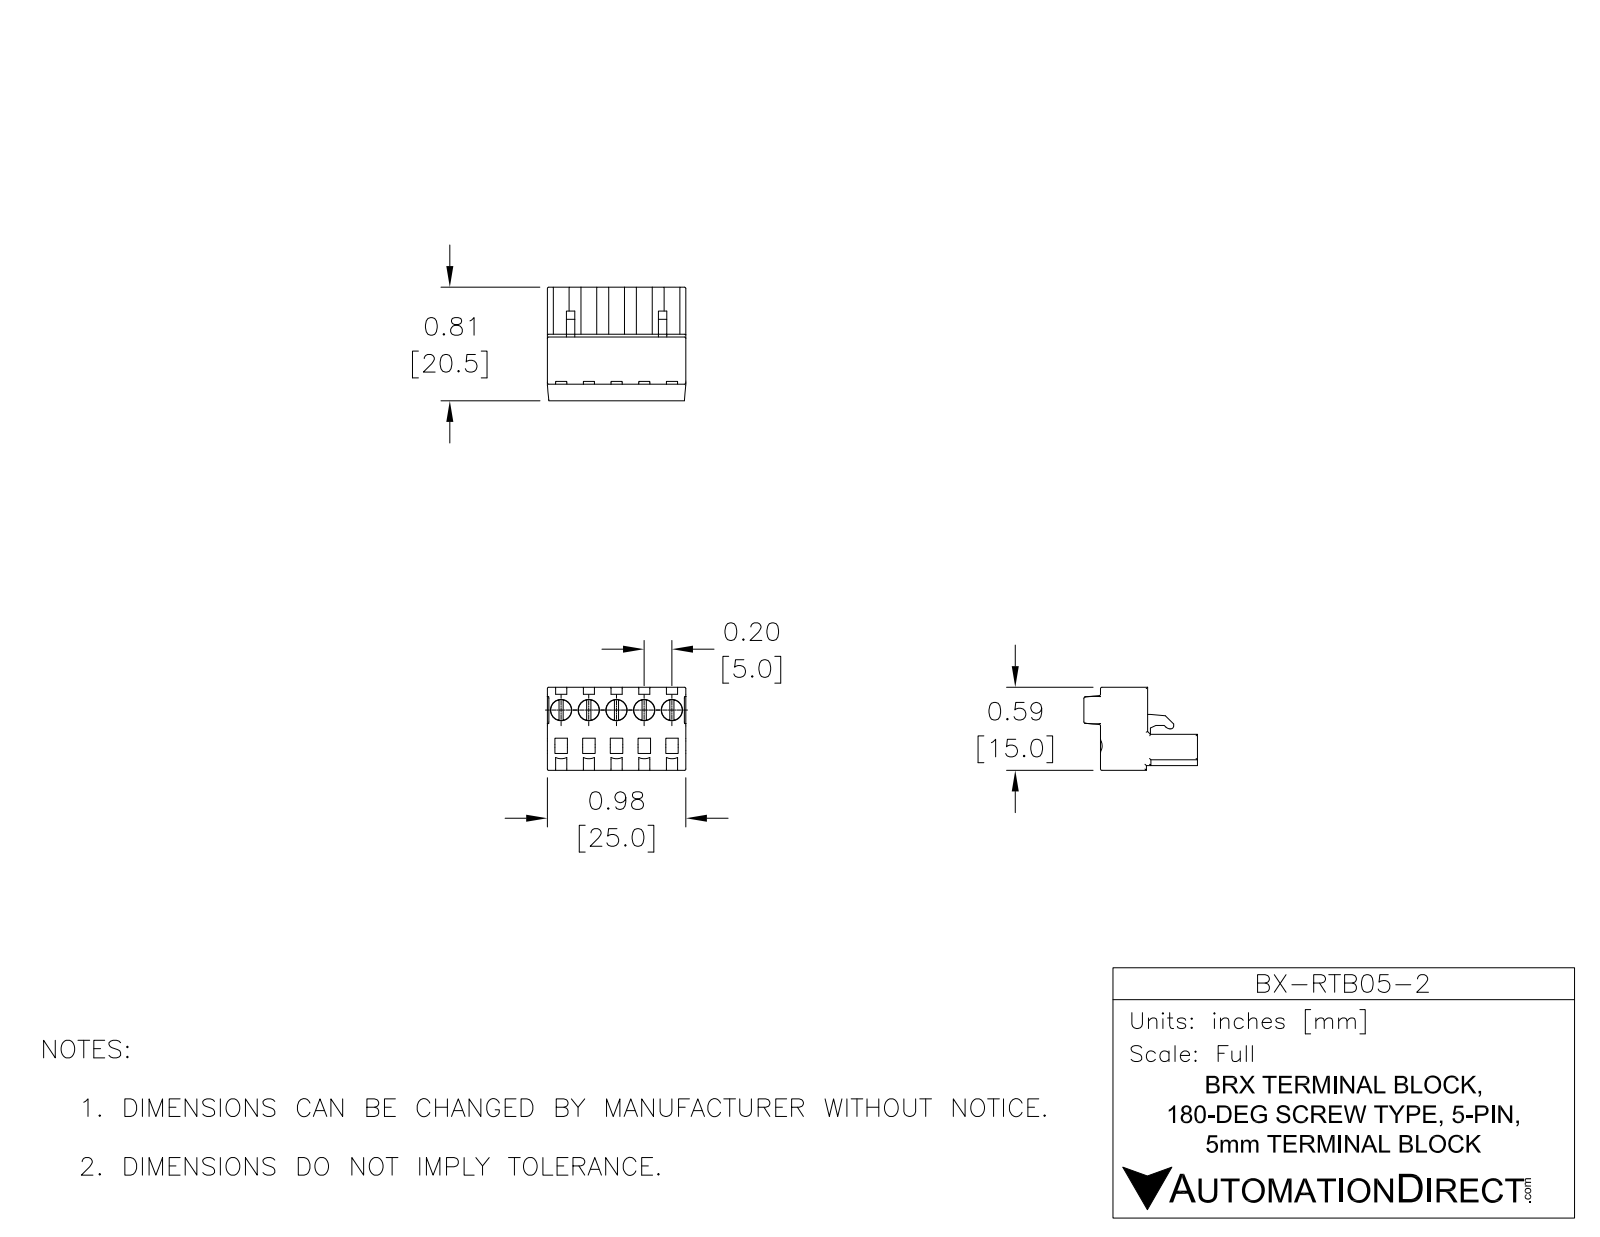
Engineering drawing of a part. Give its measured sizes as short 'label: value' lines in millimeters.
name: BX-RTB05-2
written by: SolidWorks 2016 (AUTOMOTIVE_DESIGN)
unit: mm
bodies: 1 solid, 372 faces (207 planar, 102 cylindrical, 63 other)
size: 25 × 20.5 × 15
volume: 4 195 mm³; area: 3 111 mm²
holes: 5× ⌀1.6, 5× ⌀3.15, 5× ⌀3.85
bosses: 5× ⌀3.75
rounds: 34× R0.25, 5× R2.33, 5× R2.53, 1× R0.5, 1× R1
face distances: 15, 8.5, 25, 5.7, 9.3, 9, 6.5, 0.8, 2.75, 17.5
hole spacings: 5, 10, 9.02, 15, 7.5, 12.48, 12.52, 7.49
